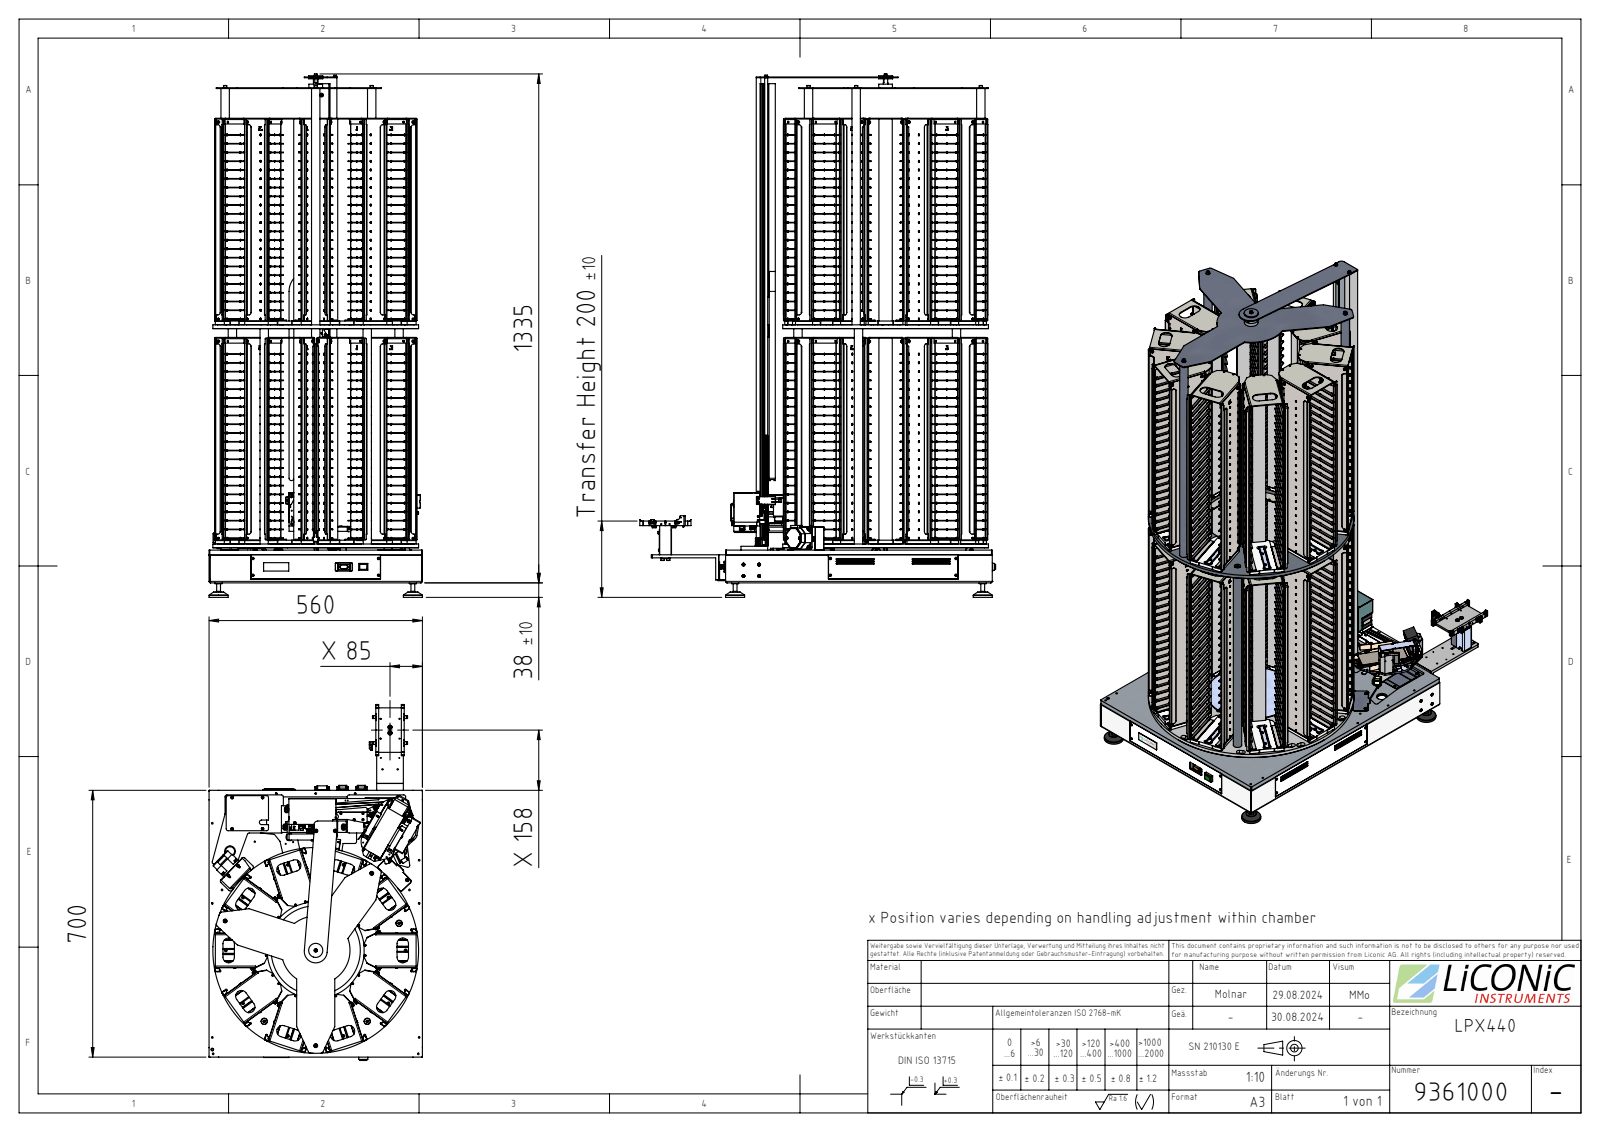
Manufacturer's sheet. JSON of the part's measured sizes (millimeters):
{"part_name": "9361000", "step_written_by": "SolidWorks 2022 (AUTOMOTIVE_DESIGN)", "units": "millimeters", "bodies": {"solids": 53, "faces": 8167, "planar": 4344, "cylindrical": 3675, "other": 148}, "overall_size": [1365.3, 933.98, 560.01], "volume_mm3": 13370000, "surface_area_mm2": 4752000, "round_holes": [[4, 88], [2.5, 59], [4.2, 58], [3.3, 47], [6.5, 21], [7.1, 16], [3.4, 10], [6.2, 10], [3.1, 8], [4.7, 8], [6.8, 8], [8, 8]], "round_bosses_or_shafts": [[22, 8], [50.01, 4], [10, 4], [1.5, 3], [540, 1], [234, 1], [15.5, 1], [14.5, 1]], "partial_cylinders_radius": [[0.1, 832], [0.25, 832], [2, 445], [5, 127], [2.5, 114], [1, 60], [1.5, 36], [3, 36]], "face_to_face_distances": [2, 10, 72, 74, 575, 12, 86, 84, 6, 1], "hole_center_spacings": [23, 46, 69, 92, 115, 138, 161, 184]}
